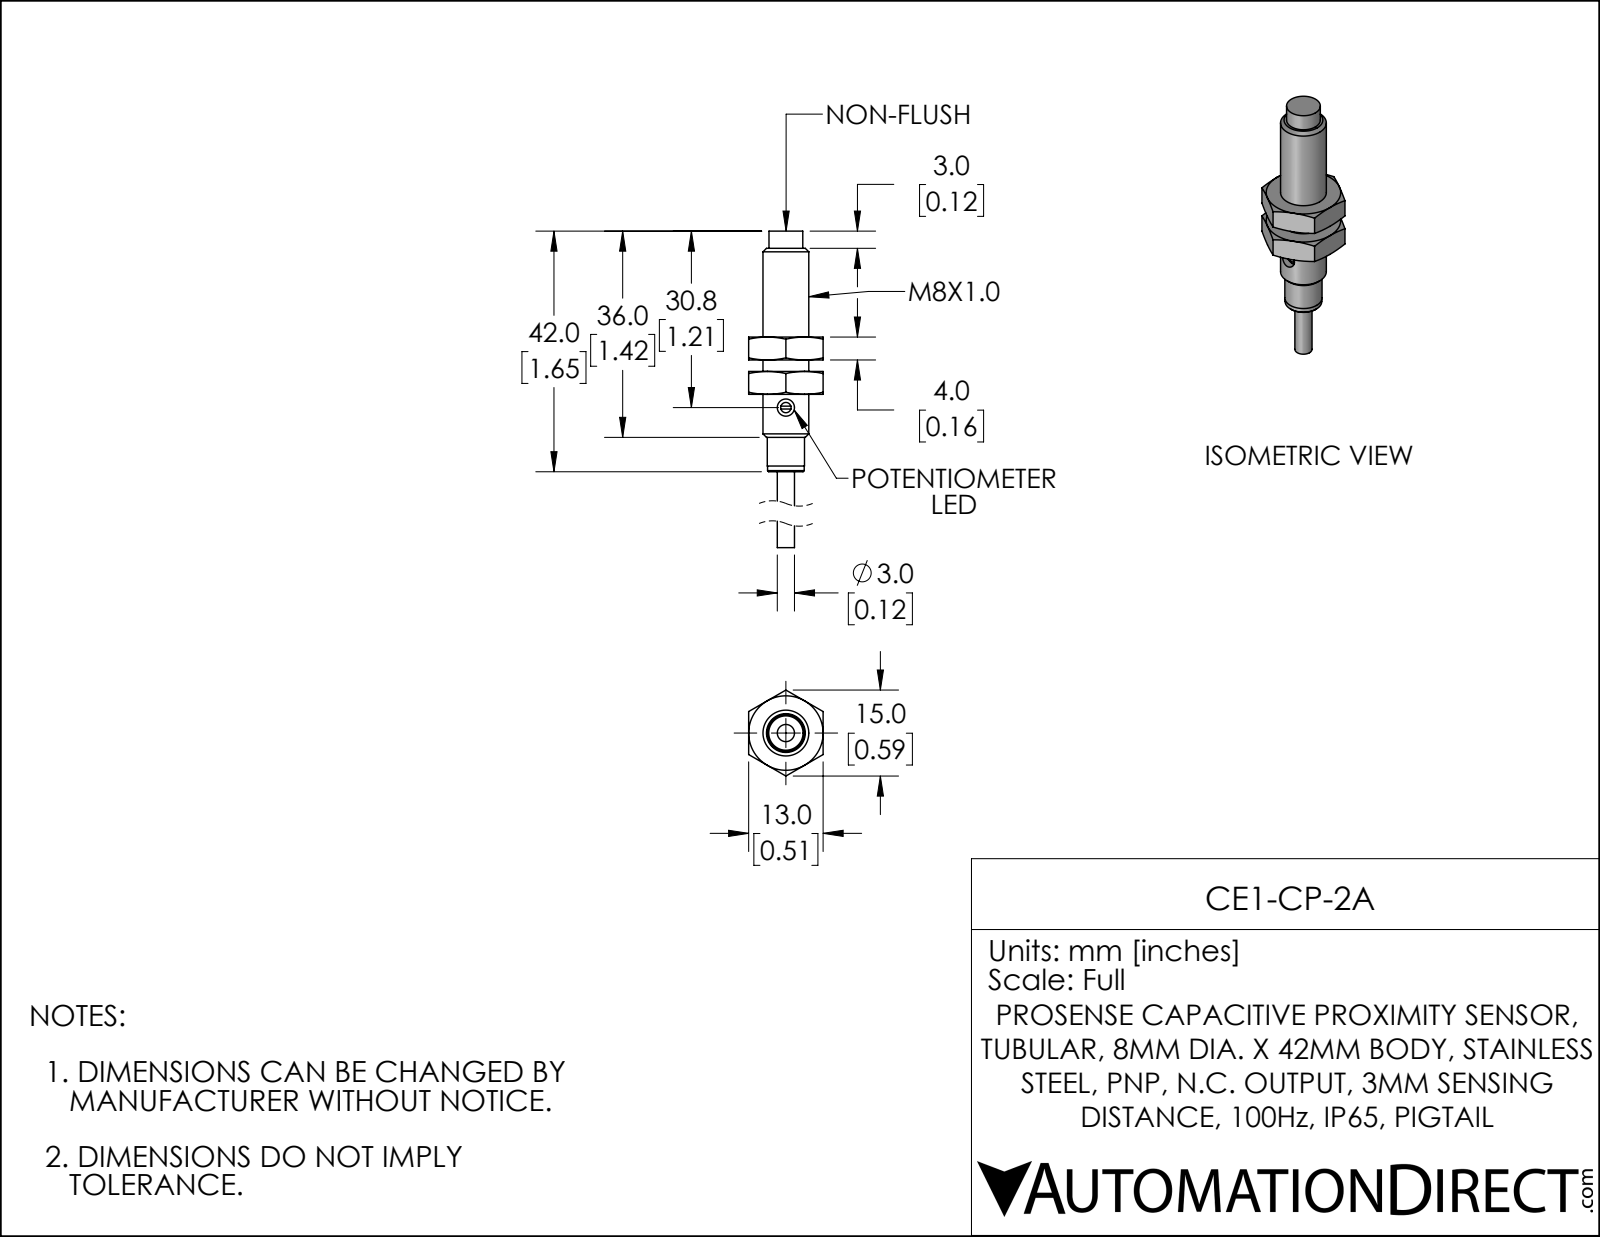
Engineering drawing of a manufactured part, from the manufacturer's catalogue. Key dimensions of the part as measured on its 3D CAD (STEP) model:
Part name (STEP PRODUCT): CE1-CP-2A
STEP written by: SolidWorks 2019 (CONFIG_CONTROL_DESIGN)
Units: inches
Bodies: 3 solids, 68 faces (28 planar, 9 cylindrical, 31 other)
Overall size (bounding box): 2.047 × 0.591 × 0.512
Volume: 0.174 in³ · Surface area: 3.281 in²
Round holes (diameter × count): ⌀0.118 ×1, ⌀0.272 ×1
Round bosses / shafts (diameter × count): ⌀0.315 ×1, ⌀0.256 ×1, ⌀0.252 ×1, ⌀0.232 ×1, ⌀0.118 ×1, ⌀0.071 ×1
Main face-to-face distances: 0.512, 0.236, 0.157, 0.394, 0.079, 0.926, 0.728, 0.885, 0.964, 1.122
